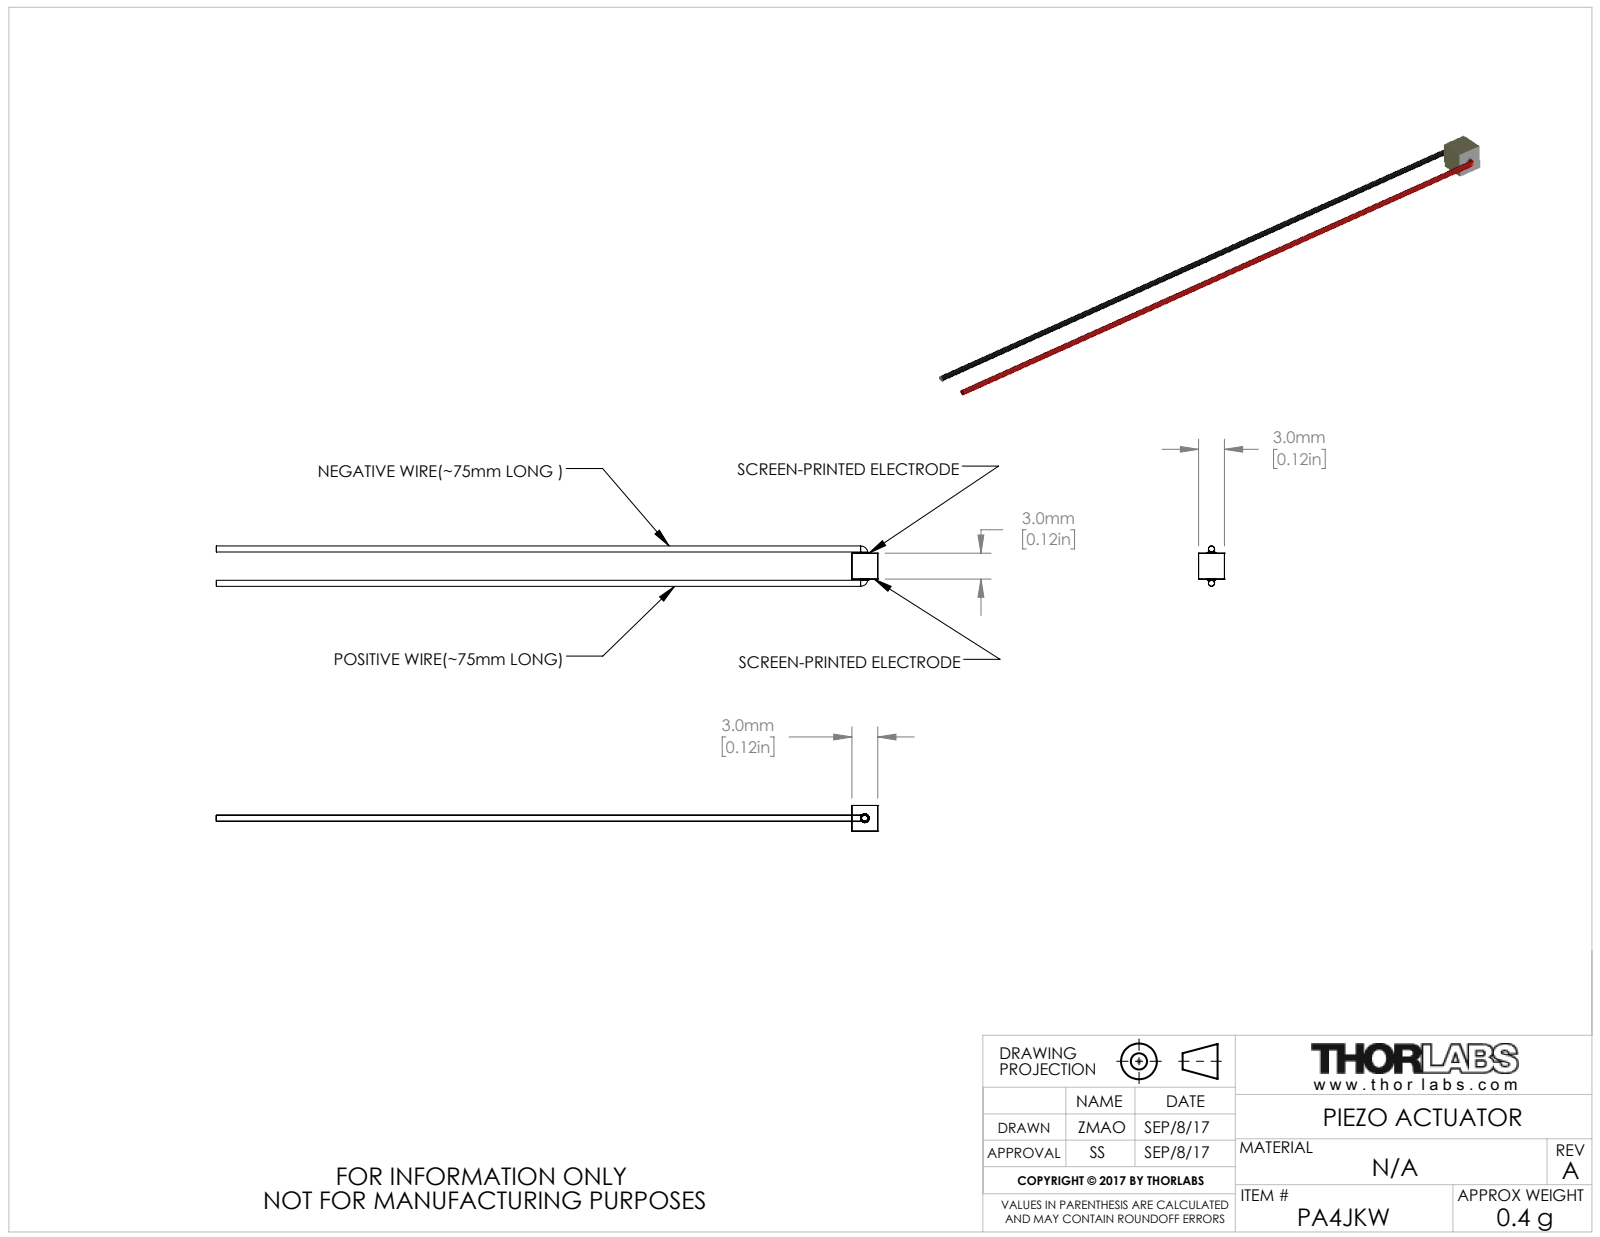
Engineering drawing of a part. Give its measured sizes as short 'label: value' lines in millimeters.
name: CTN011268
written by: SolidWorks 2016 (AUTOMOTIVE_DESIGN)
unit: mm
bodies: 1 solid, 22 faces (10 planar, 8 cylindrical, 4 other)
size: 77 × 4.7 × 3
volume: 85 mm³; area: 387 mm²
bosses: 2× ⌀0.7, 1× ⌀1
face distances: 3, 3.1, 74, 77, 3.2
